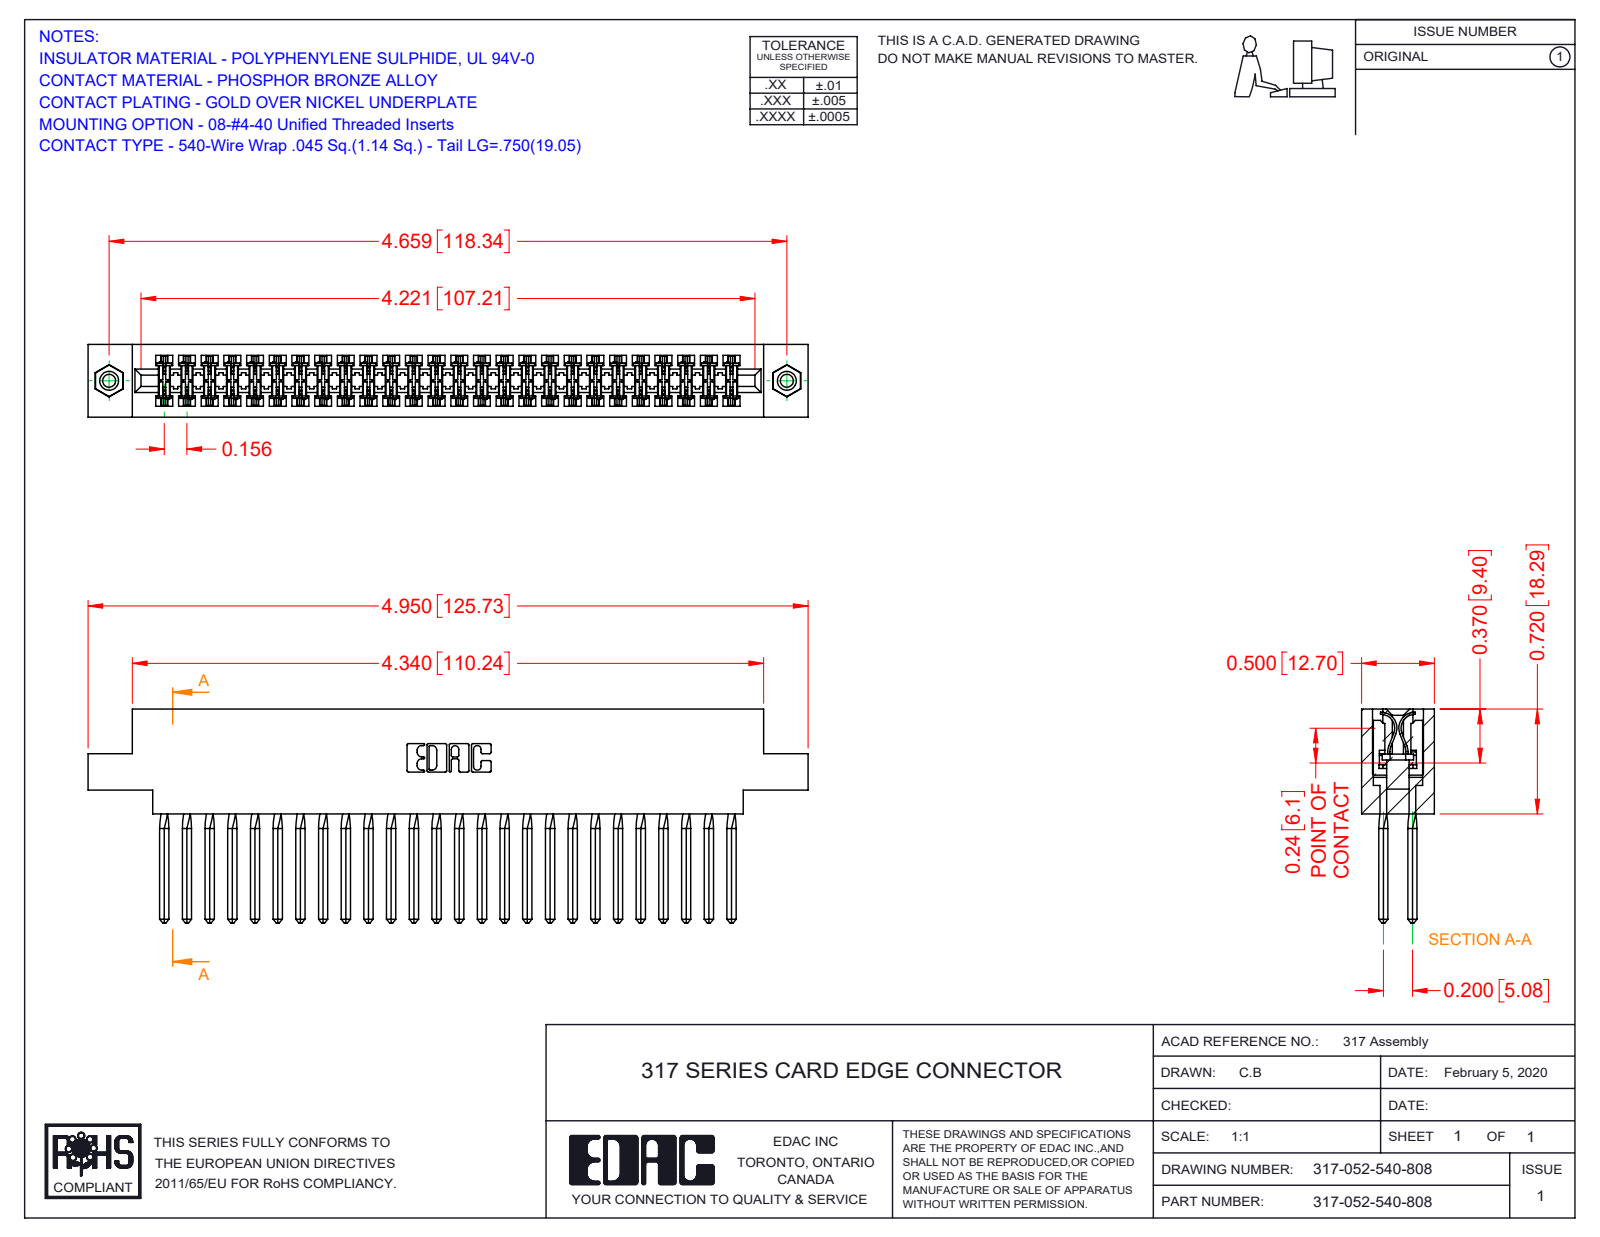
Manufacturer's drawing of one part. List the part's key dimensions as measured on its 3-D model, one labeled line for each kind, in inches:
Part name (STEP PRODUCT): 317-052-540-878; 317 Part_.156 Dia - TI; 317-290-001_540; 345-250-001_345-250-003-102
STEP written by: SolidWorks 2016 (CONFIG_CONTROL_DESIGN)
Units: inches
Bodies: 55 solids, 4790 faces (3886 planar, 680 cylindrical, 224 other)
Overall size (bounding box): 4.95 × 1.47 × 0.5
Volume: 1.254 in³ · Surface area: 46.6 in²
Round holes (diameter × count): ⌀0.089 ×2, ⌀0.125 ×2, ⌀0.156 ×2
Round bosses / shafts (diameter × count): ⌀0.155 ×2
Partial cylindrical surfaces — rounded edges, fillets, slot ends (radius × count): R0.015 ×104, R0.01 ×22, R0.007 ×6, R0.031 ×6, R0.026 ×3, R0.095 ×2, R0.1 ×2, R0.11 ×2
Main face-to-face distances: 0.5, 0.075, 0.425, 0.35, 0.11, 0.195, 0.094, 0.2, 0.72, 0.115
Hole centre spacings: 4.659
